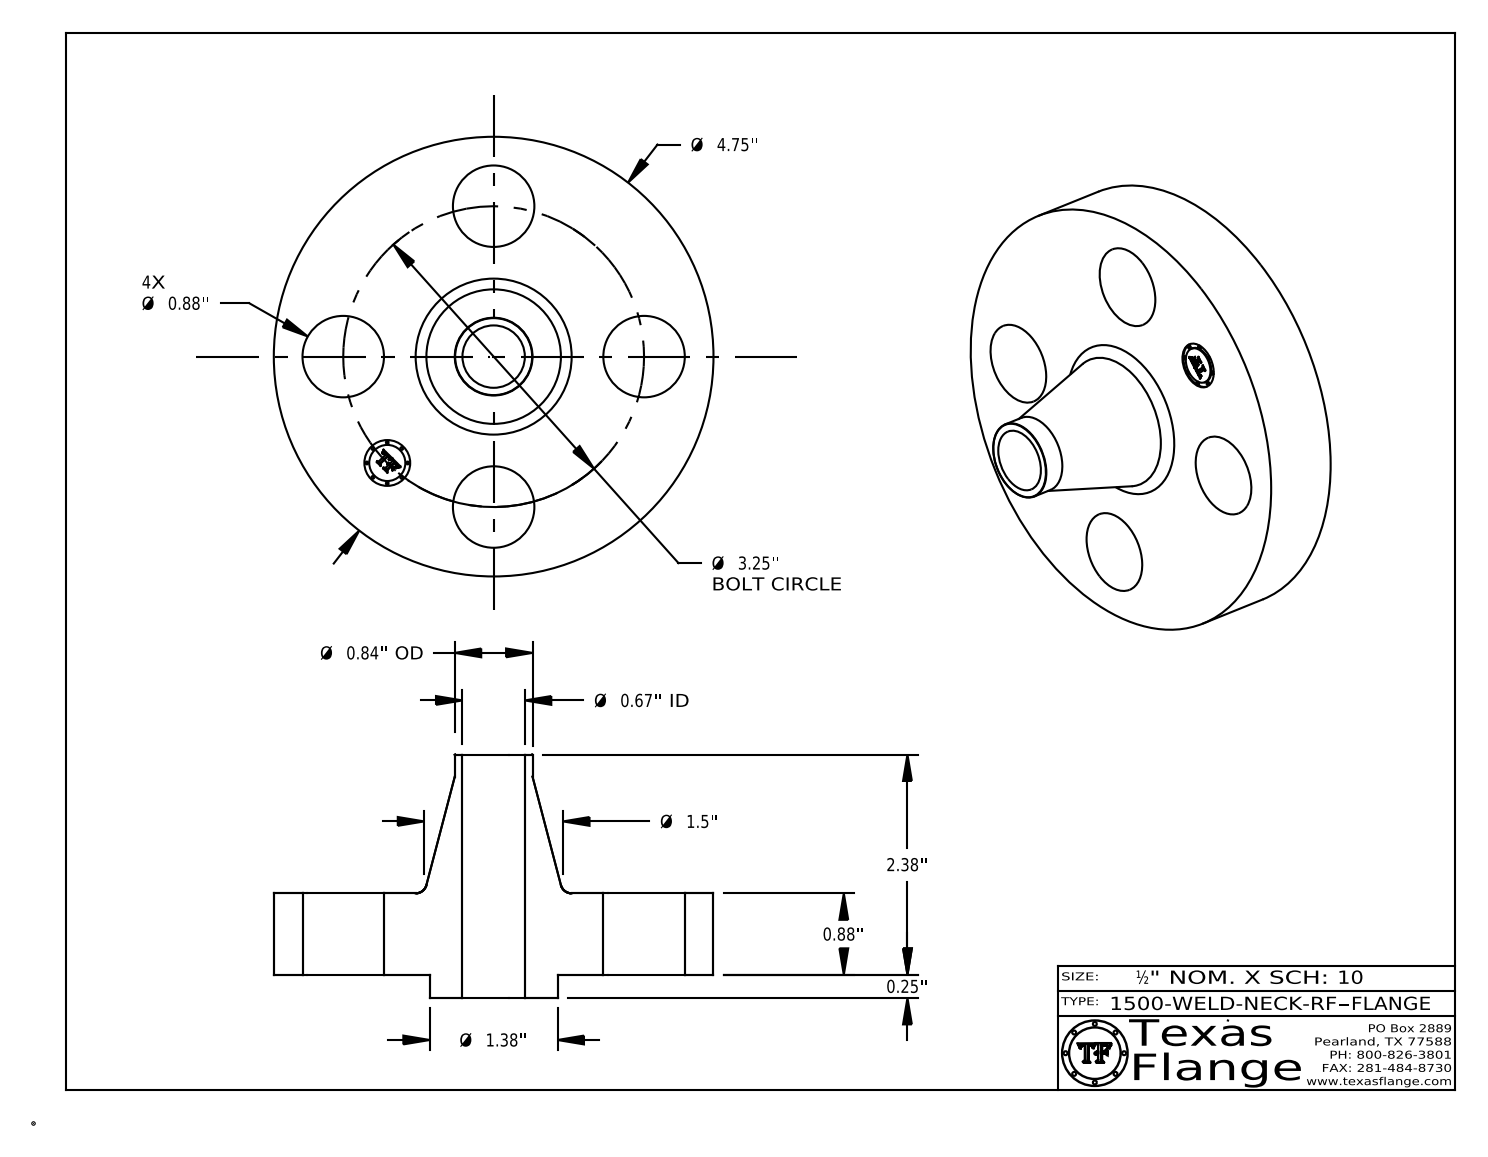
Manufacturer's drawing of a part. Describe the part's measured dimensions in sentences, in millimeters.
The part is named "1500-WELD-NECK-RF". Its 3-D file was written by "CATIA V5 STEP AP214 (AUTOMOTIVE_DESIGN)". It is 1 solid with 411 faces: 369 planar, 36 cylindrical and 6 other. Overall it measures 120.7 by 120.7 by 66.8 millimeters. Its volume is 236 300 cubic millimeters and its surface area 41 000 square millimeters. Round holes: 4 of diameter 22.4, 1 of diameter 12.6, 1 of diameter 17.1. Round bosses or shafts: 8 of diameter 0.8, 1 of diameter 120.7, 1 of diameter 35.1, 1 of diameter 21.3, 1 of diameter 9.9. The main face-to-face distances are 22.4, 6.4, 28.7, 66.8, 60.5, 38.1, 28.3, 22, 0.4, 38.5. The hole center spacings are 41.3, 58.4, 31.6, 76.3, 82.6.
